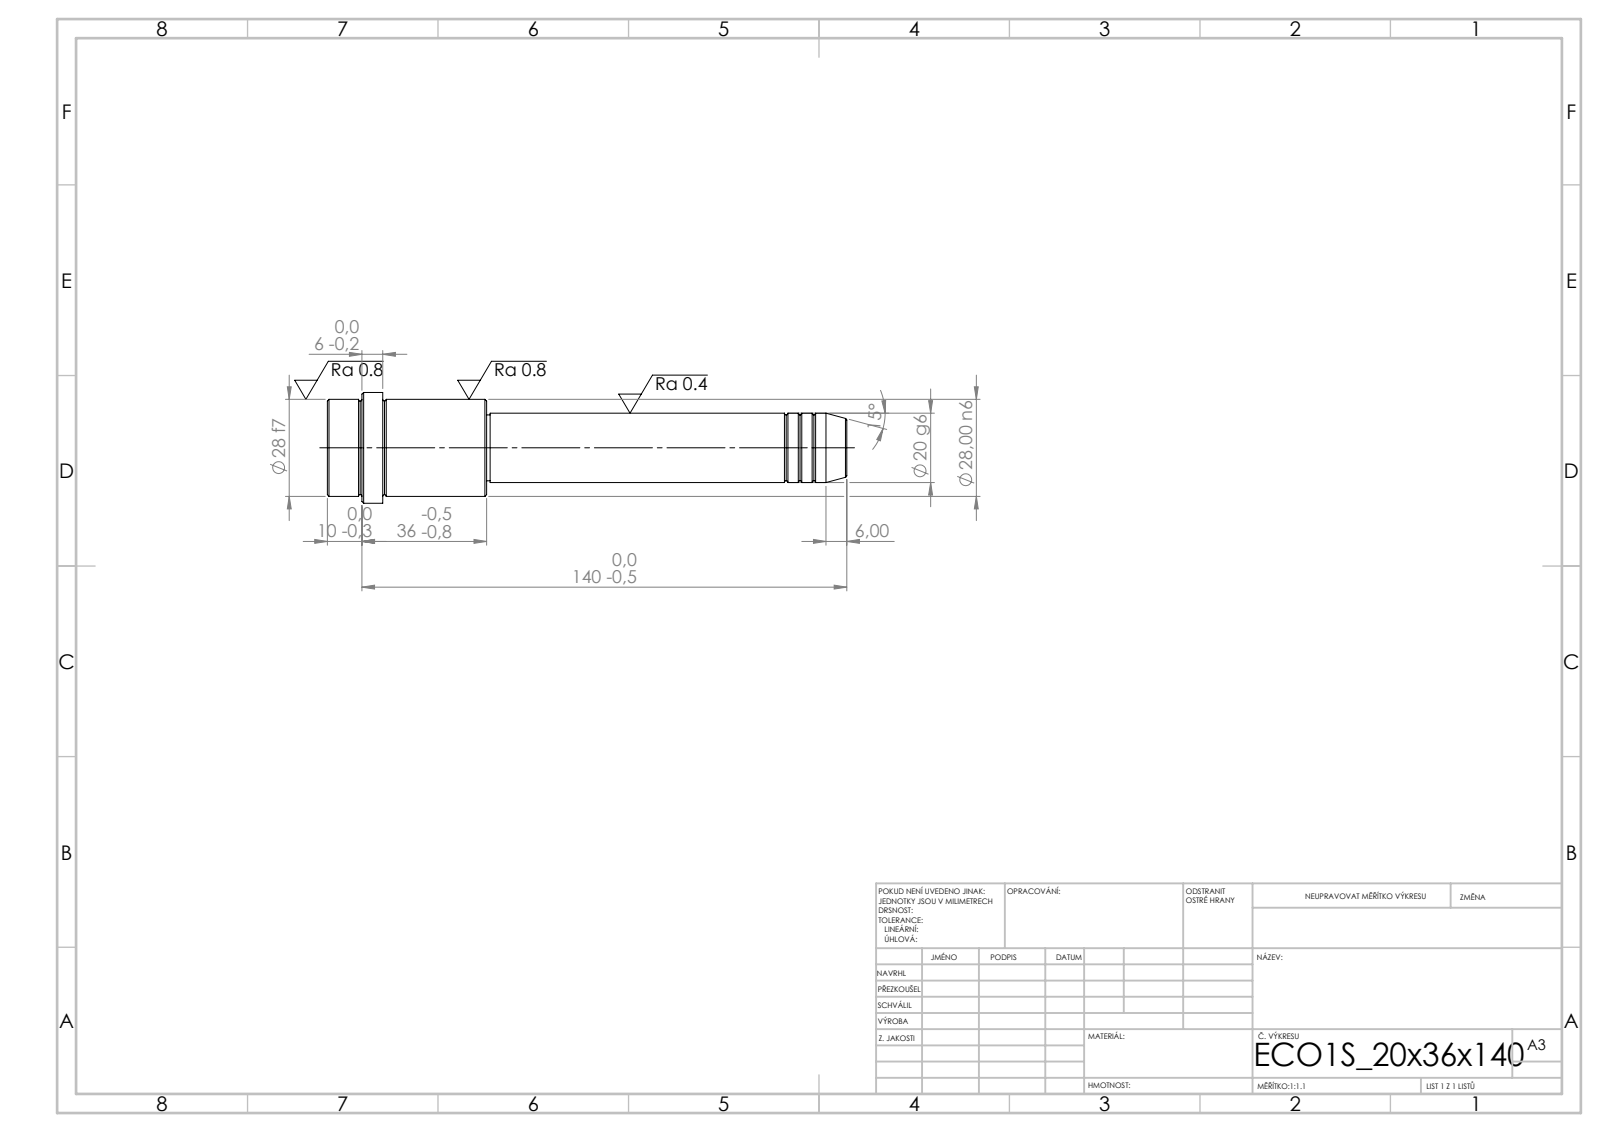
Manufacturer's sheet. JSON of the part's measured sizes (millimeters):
{"step_written_by": "SolidWorks 2019 (CONFIG_CONTROL_DESIGN)", "units": "millimeters", "bodies": {"solids": 1, "faces": 52, "planar": 6, "cylindrical": 16, "other": 30}, "overall_size": [150, 32, 32], "volume_mm3": 61635, "surface_area_mm2": 12316, "round_bosses_or_shafts": [[32, 1], [28, 1], [20, 1], [19, 1]], "face_to_face_distances": [46, 104, 150, 134, 30, 16, 140, 36, 6, 10]}
